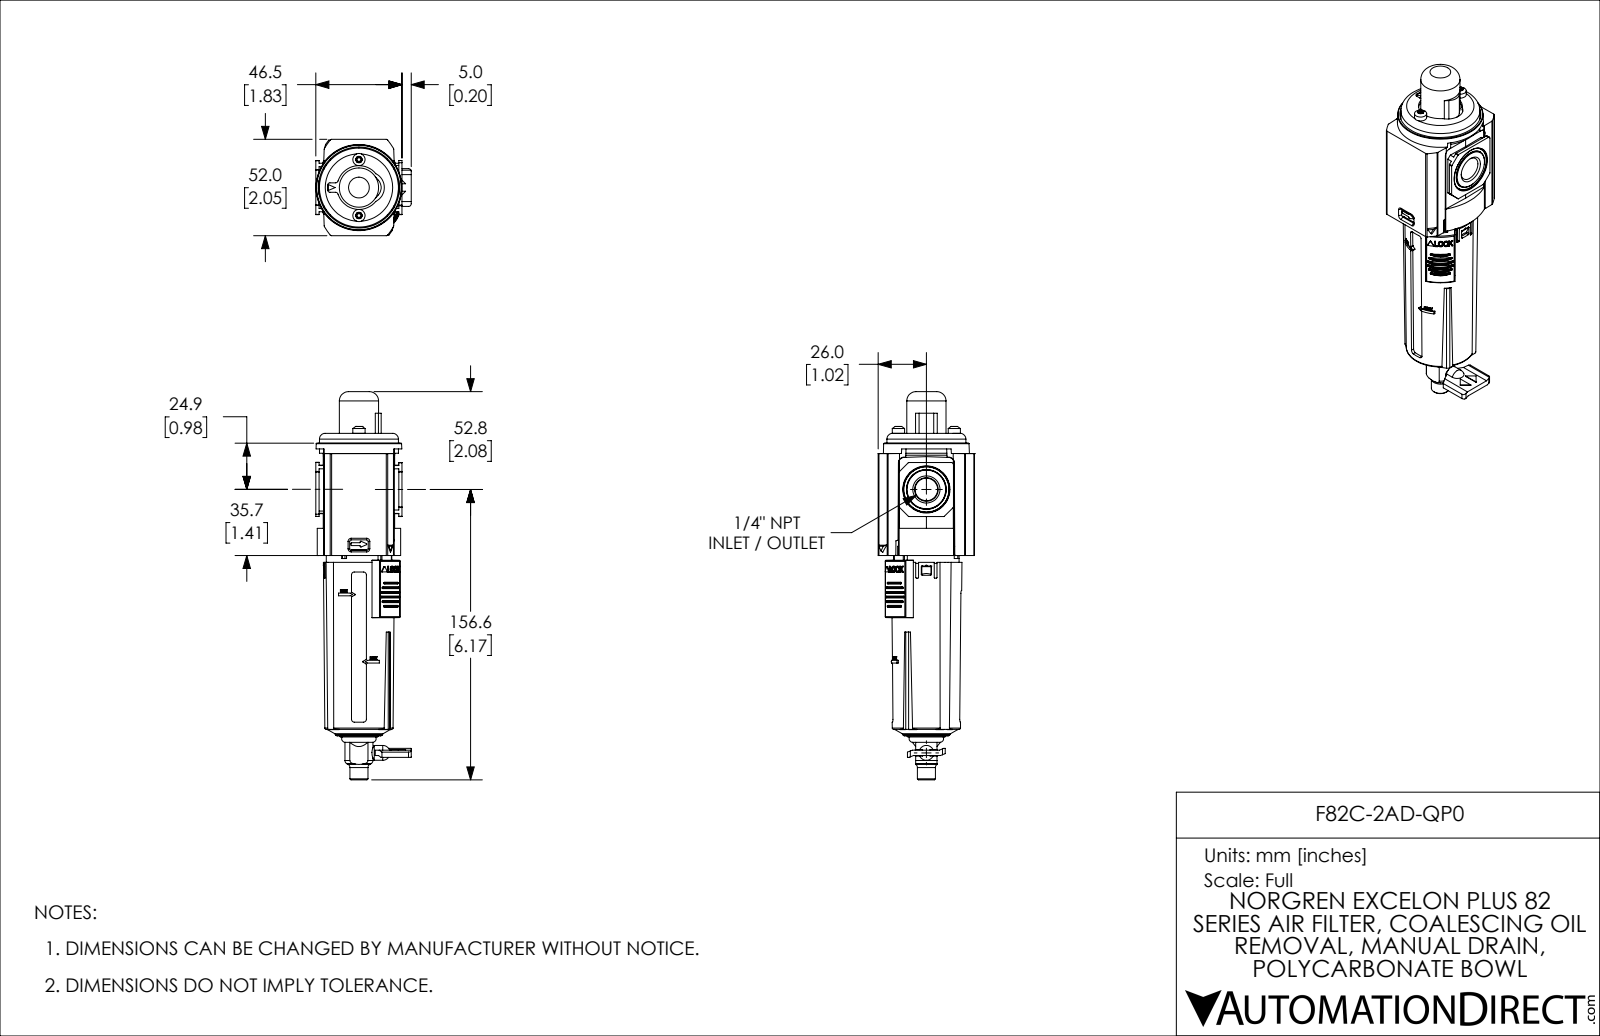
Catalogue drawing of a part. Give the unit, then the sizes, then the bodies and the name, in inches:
Units: inches
Overall size (bounding box): 8.245 × 2.047 × 2.027
Round holes (diameter × count): ⌀0.059 ×2, ⌀0.079 ×2, ⌀0.128 ×2, ⌀0.173 ×2, ⌀0.25 ×1, ⌀0.63 ×1
Round bosses / shafts (diameter × count): ⌀0.26 ×2, ⌀0.157 ×2, ⌀1.678 ×1, ⌀1.524 ×1, ⌀1.388 ×1, ⌀1.356 ×1, ⌀1.291 ×1, ⌀1.257 ×1
Partial cylindrical surfaces — rounded edges, fillets, slot ends (radius × count): R0.02 ×78, R0.039 ×30, R0.012 ×11, R0.008 ×10, R0.01 ×10, R0.031 ×8, R0.036 ×8, R0.048 ×8
Main face-to-face distances: 0.059, 1.988, 2.047, 1.929, 1.896, 0.236, 0.182, 1.352, 1.475, 0.123
Hole centre spacings: 0.797, 0.531, 0.594, 0.594, 1.189, 1.063, 1.188, 1.189
Volume: 14.71 in³ · Surface area: 95.89 in²
Bodies: 8 solids, 1233 faces (542 planar, 468 cylindrical, 223 other)
Part name (STEP PRODUCT): F82C-2AD-QP0
STEP written by: SolidWorks 2021 (CONFIG_CONTROL_DESIGN)
